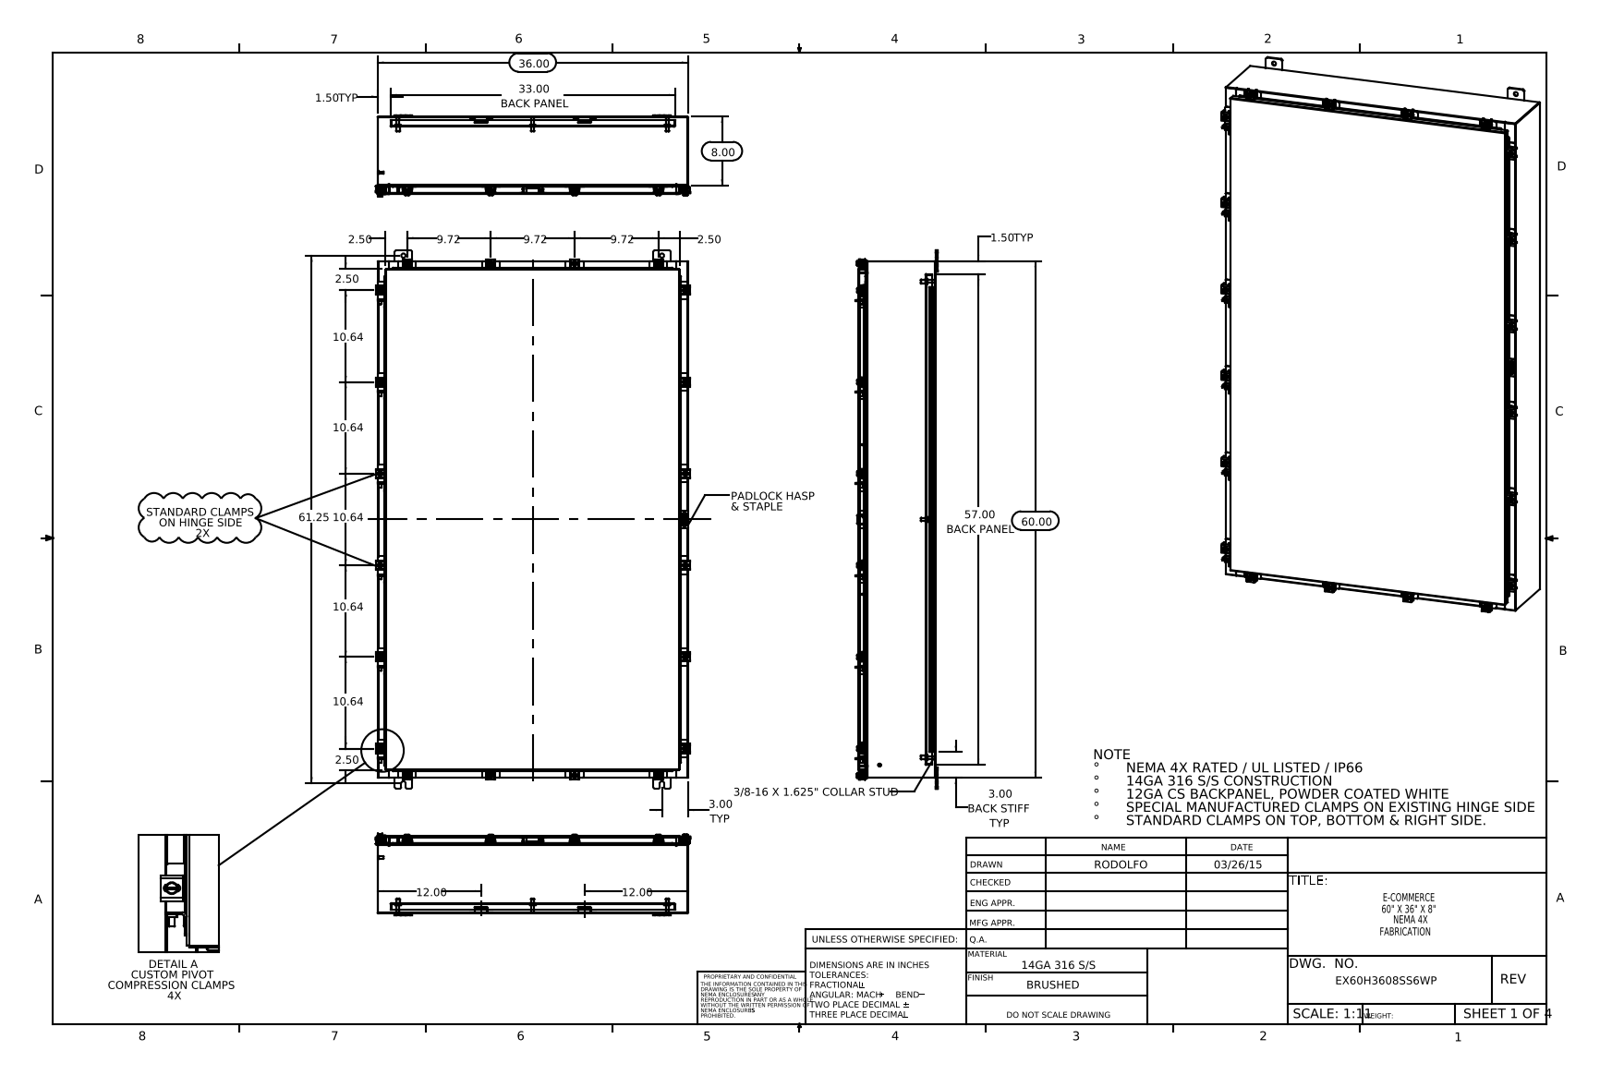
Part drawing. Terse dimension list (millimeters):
name: Special Clamp Assembly; 10_30 CD Stud; EX60H3608SS6WP; EX60H3608SS6WP Clamp Assembly (+8 more)
written by: SolidWorks 2014 (CONFIG_CONTROL_DESIGN)
unit: mm
bodies: 144 solids, 3524 faces (1841 planar, 1347 cylindrical, 336 other)
size: 1587.5 × 925.1 × 240.1
volume: 12 060 000 mm³; area: 11 720 000 mm²
holes: 20× ⌀5.4, 20× ⌀6.6, 12× ⌀12.7, 9× ⌀6.4, 1× ⌀3.2
bosses: 20× ⌀12.7, 20× ⌀6.4, 14× ⌀10.1, 8× ⌀15.9, 8× ⌀9.5, 8× ⌀8.4, 8× ⌀4, 8× ⌀3.6
rounds: 78× R1.5, 40× R3.6, 38× R0.3, 38× R2.3, 34× R2.2, 34× R3, 33× R1.3, 32× R3.7
face distances: 1.9, 226.1, 224.2, 228, 2.6, 25.4, 27.3, 198.8, 200.7, 29.9
hole spacings: 50, 56.5, 59.6, 354.9, 374.1, 409.6, 701.7, 755.5
